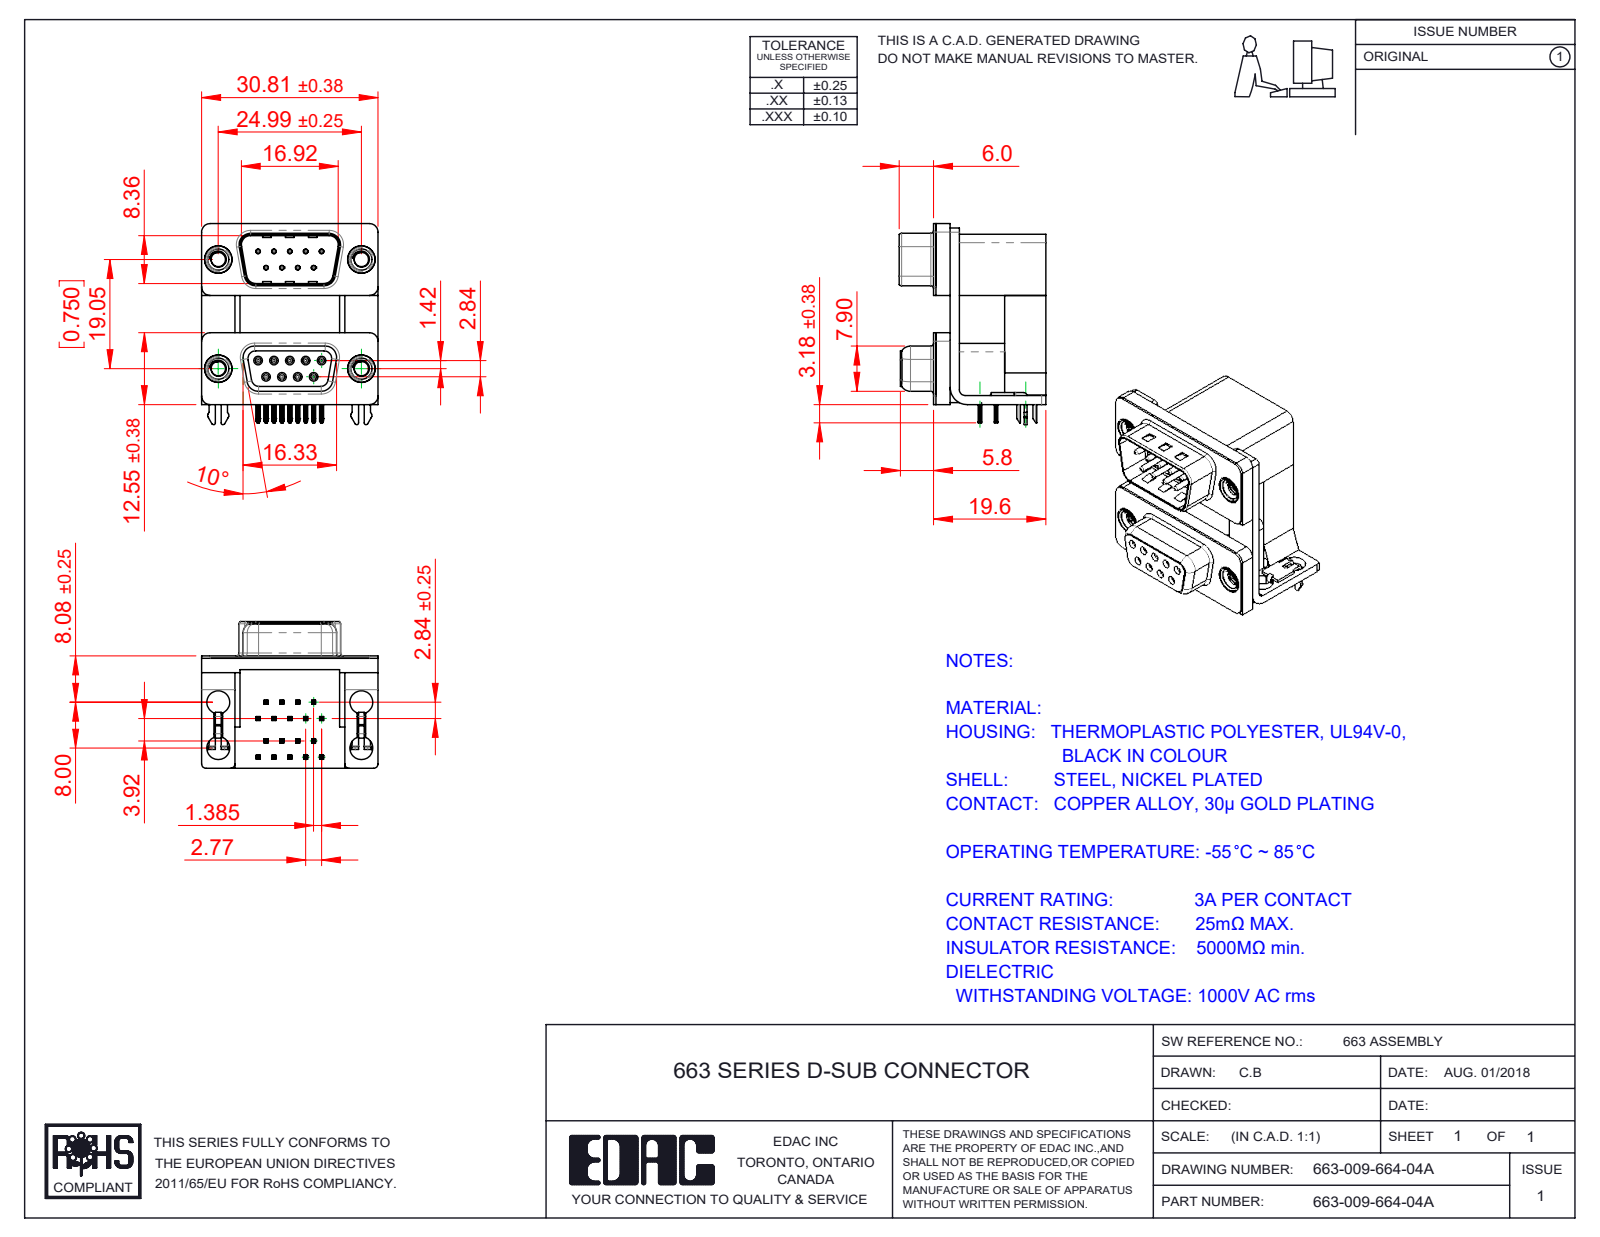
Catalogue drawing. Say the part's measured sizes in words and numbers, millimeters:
The part is named "663 Housing Spacer_09 Contacts M; 663 Housing Upper_09 Contacts M; 663 Contact Bottom Lower; 663 Mounting Bracket_2ProngM (+8 more)". Its 3-D file was written by "SolidWorks 2020 (CONFIG_CONTROL_DESIGN)". It is 31 solids with 2641 faces: 1341 planar, 733 cylindrical and 567 other. Overall it measures 35.1 by 30.81 by 25.6 millimeters. Its volume is 10 795 cubic millimeters and its surface area 12 657 square millimeters. Round holes: 18 of diameter 0.8, 9 of diameter 0.35, 9 of diameter 0.9, 8 of diameter 4, 4 of diameter 2.5, 4 of diameter 3.5, 4 of diameter 4.8, 4 of diameter 5. Round bosses or shafts: 9 of diameter 1.2, 9 of diameter 0.75, 4 of diameter 4.9, 4 of diameter 4.75, 4 of diameter 3.9. Partial cylindrical surfaces (rounded edges, fillets, slot ends): 73 of radius 0.1, 42 of radius 0.25, 36 of radius 0.15, 18 of radius 0.12, 18 of radius 0.35, 16 of radius 0.5, 15 of radius 1.5, 10 of radius 0.75. The main face-to-face distances are 0.4, 2.5, 16.7, 19.2, 7.2, 9.5, 12, 1.6, 19.6, 12.4. The hole center spacings are 3.16, 2.77, 19.25, 19.05, 5.54, 19.84, 16.27, 21.93.
